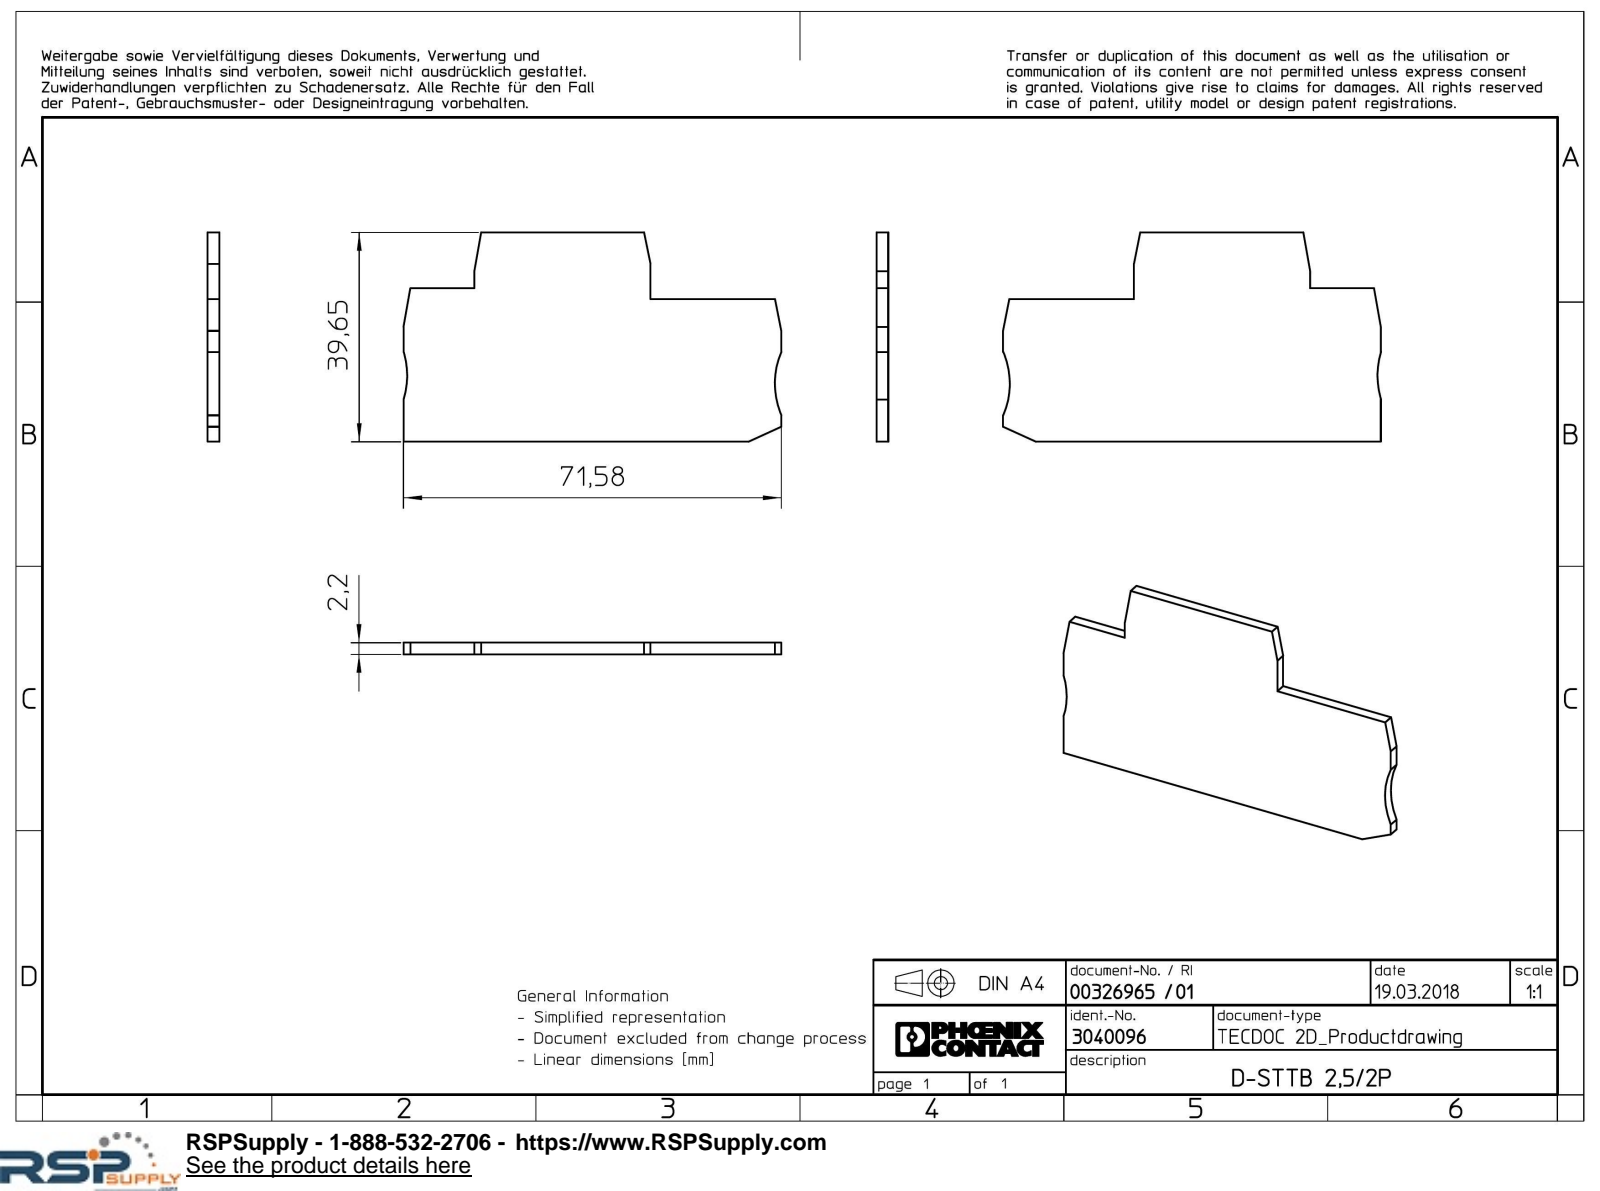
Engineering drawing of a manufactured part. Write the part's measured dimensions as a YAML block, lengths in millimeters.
part_name: "D_STTB_25_2P_SELECT"
step_written_by: "Creo Elements/Direct Modeling 18.1I 14-Aug-2016 (C) Parametric Technology GmbH (AUTOMOTIVE_DESIGN)"
units: millimeters
bodies: {solids: 1, faces: 19, planar: 17, cylindrical: 2, other: 0}
overall_size: [71.58, 39.65, 2.2]
volume: 5153
surface_area: 5160
partial_cylinders:
  - {radius: 15, count: 2}
face_to_face_distances: [2.2, 39.65, 27, 12.65, 29.05, 2.05, 10.6, 11.36, 46.77, 71.57]
